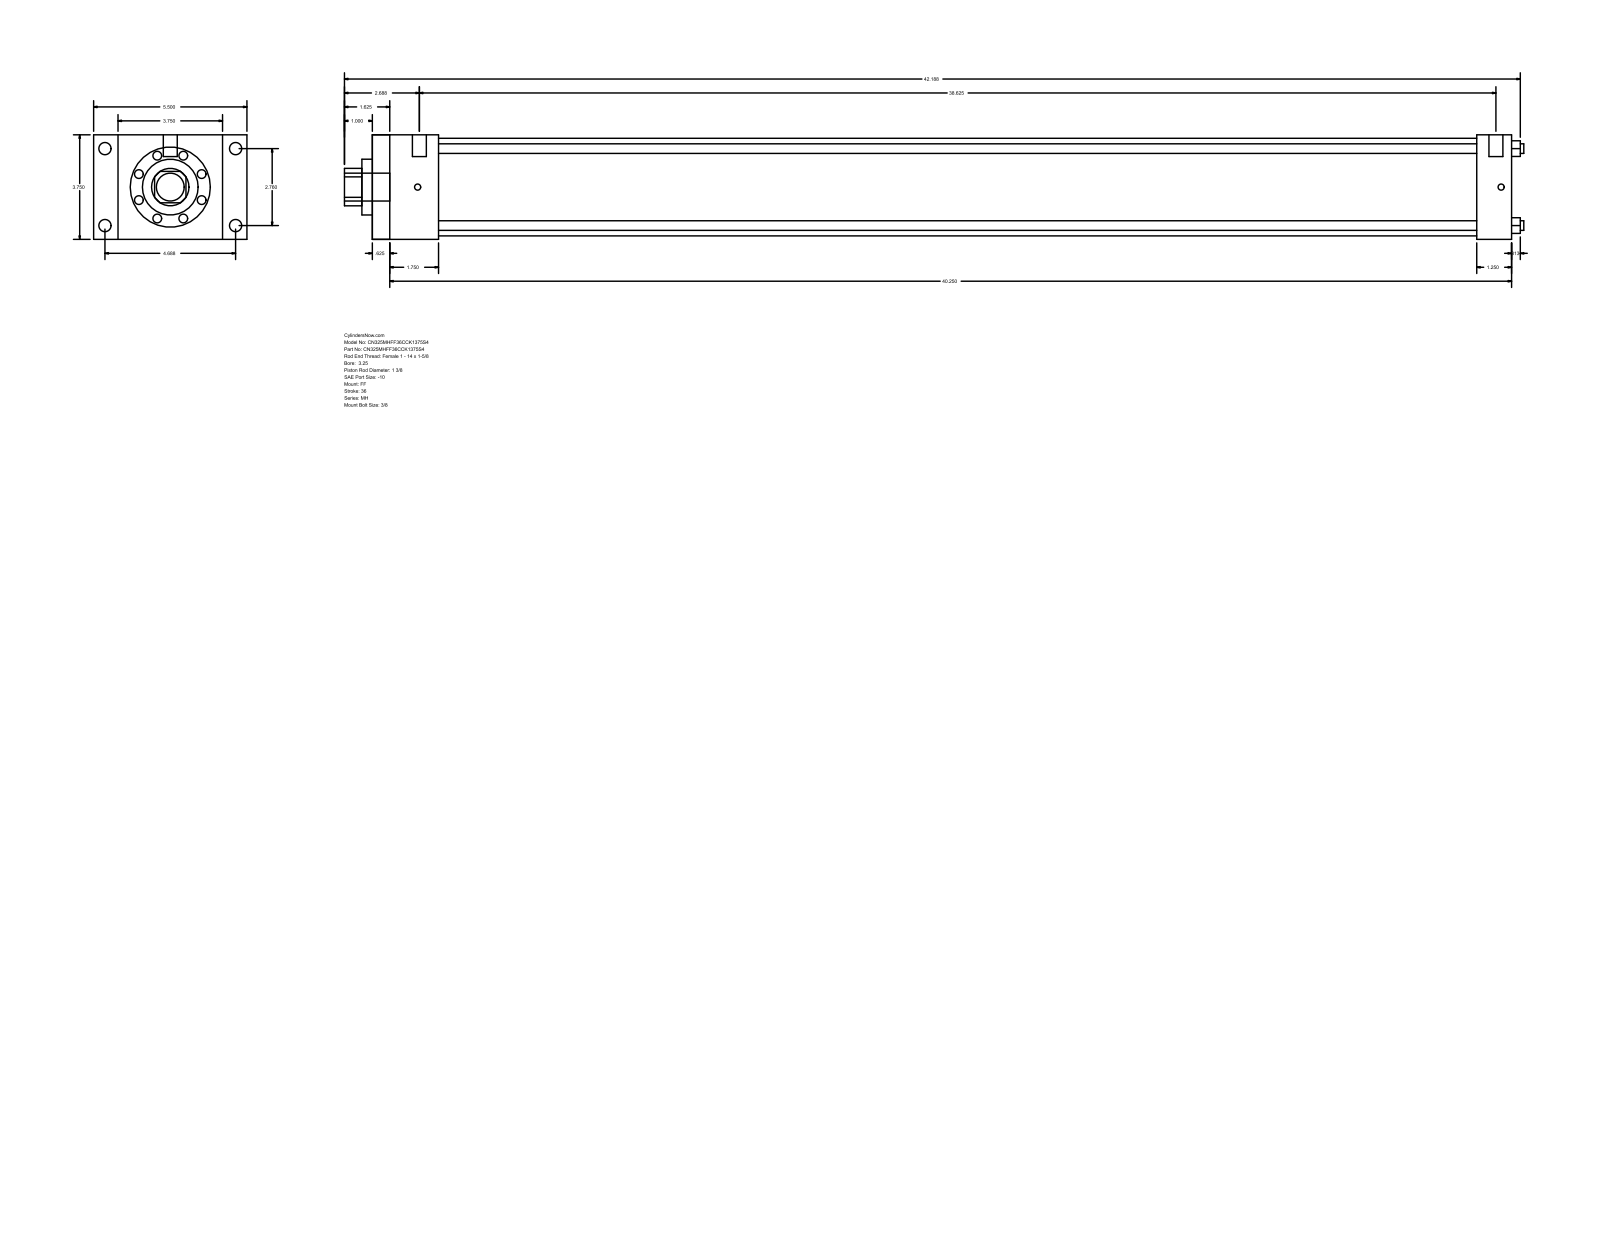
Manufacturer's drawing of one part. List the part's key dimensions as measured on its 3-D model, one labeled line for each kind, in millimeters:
Part name (STEP PRODUCT): MH_FF__0325_1.375
STEP written by: GSSL Pune (CONFIG_CONTROL_DESIGN)
Units: millimetres
Bodies: 0 solids, 92 faces (64 planar, 28 cylindrical, 0 other)
Overall size (bounding box): 1074.74 × 139.7 × 95.25
Round holes (diameter × count): ⌀8.76 ×4, ⌀34.92 ×1, ⌀50.8 ×1, ⌀88.9 ×1
Round bosses / shafts (diameter × count): ⌀11.13 ×4, ⌀5.56 ×4, ⌀12.7 ×2, ⌀25.4 ×1
Partial cylindrical surfaces — rounded edges, fillets, slot ends (radius × count): R17.06 ×1
Main face-to-face distances: 95.24, 1038.22, 15.87, 1022.35, 22.23, 117.47, 1006.48, 990.61, 31.74, 60.32
Hole centre spacings: 49.57, 70.1, 99.14
